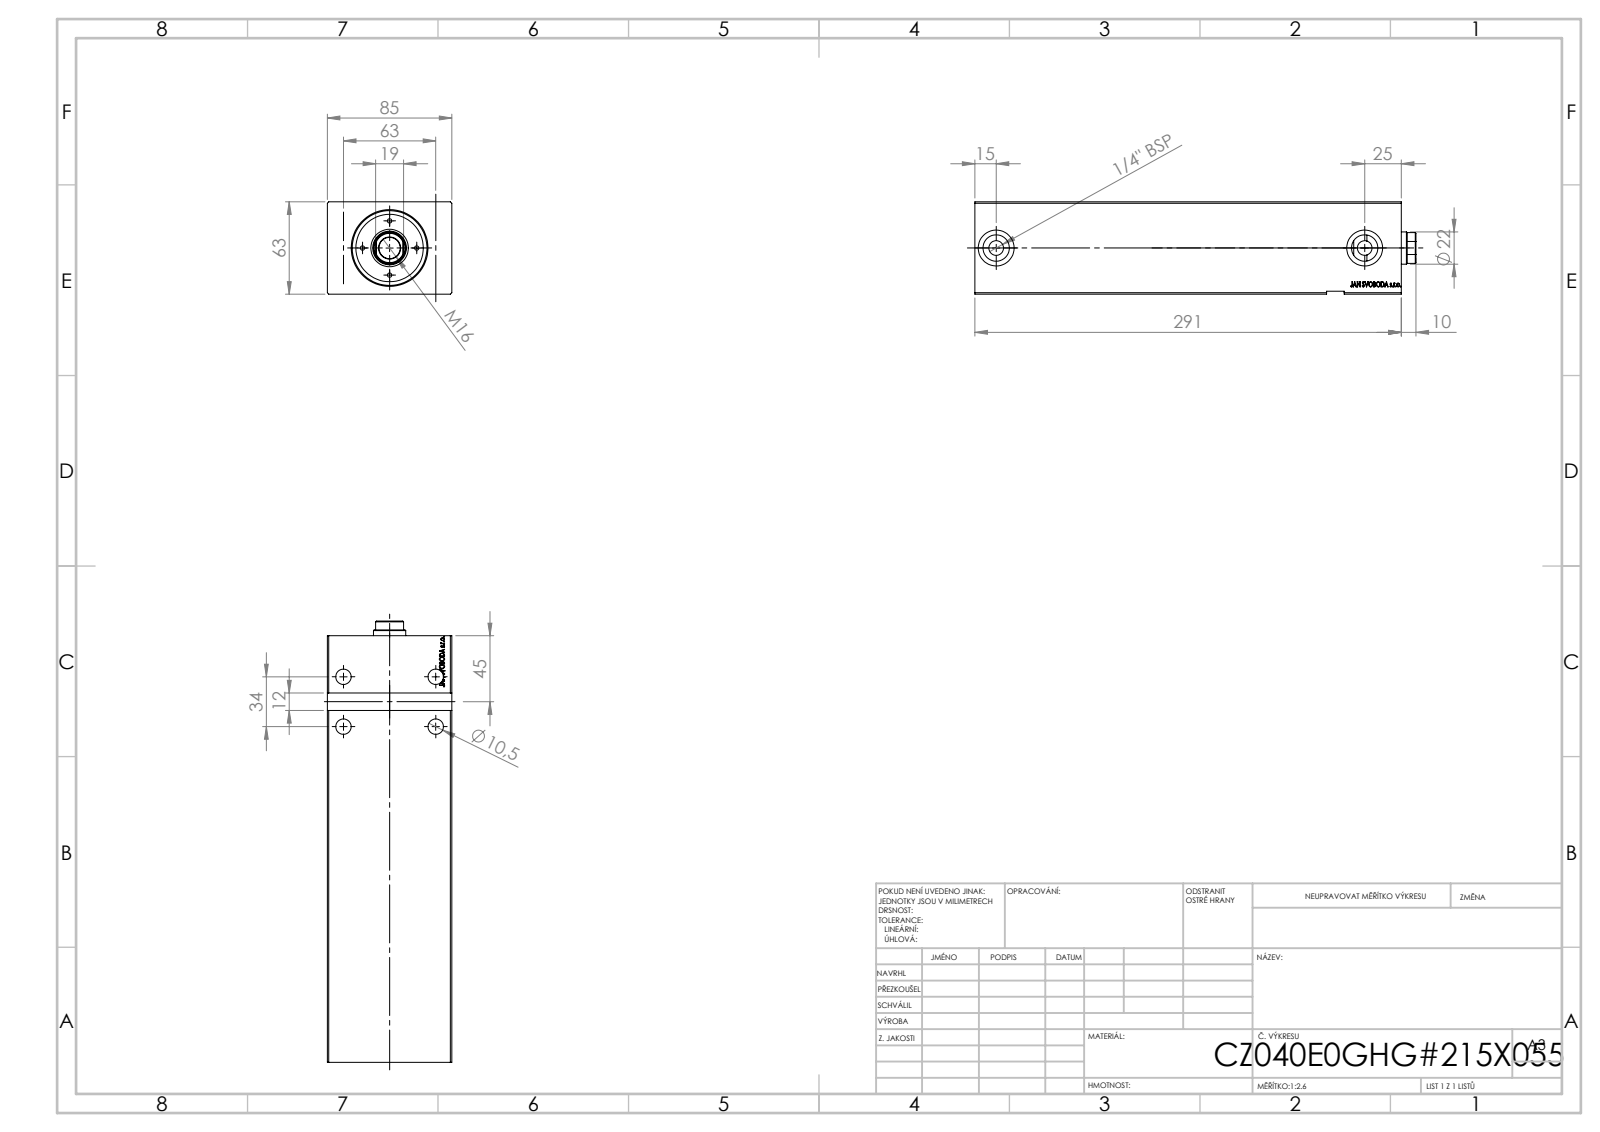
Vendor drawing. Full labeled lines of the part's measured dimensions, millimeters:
STEP written by: SolidWorks 2019 (CONFIG_CONTROL_DESIGN)
Units: millimetres
Bodies: 1 solid, 781 faces (384 planar, 31 cylindrical, 366 other)
Overall size (bounding box): 291 × 85 × 63
Volume: 1 172 000 mm³ · Surface area: 140 557 mm²
Round holes (diameter × count): ⌀10.5 ×4, ⌀8 ×2, ⌀10 ×2, ⌀18 ×2, ⌀24.5 ×2, ⌀36 ×1, ⌀40 ×1, ⌀51 ×1
Main face-to-face distances: 63, 85, 291, 275.7, 15.3, 2, 61, 290.8, 15.1, 103.22
Hole centre spacings: 34, 63, 71.59, 18.85, 32.18, 46.04, 52.91, 205.25
